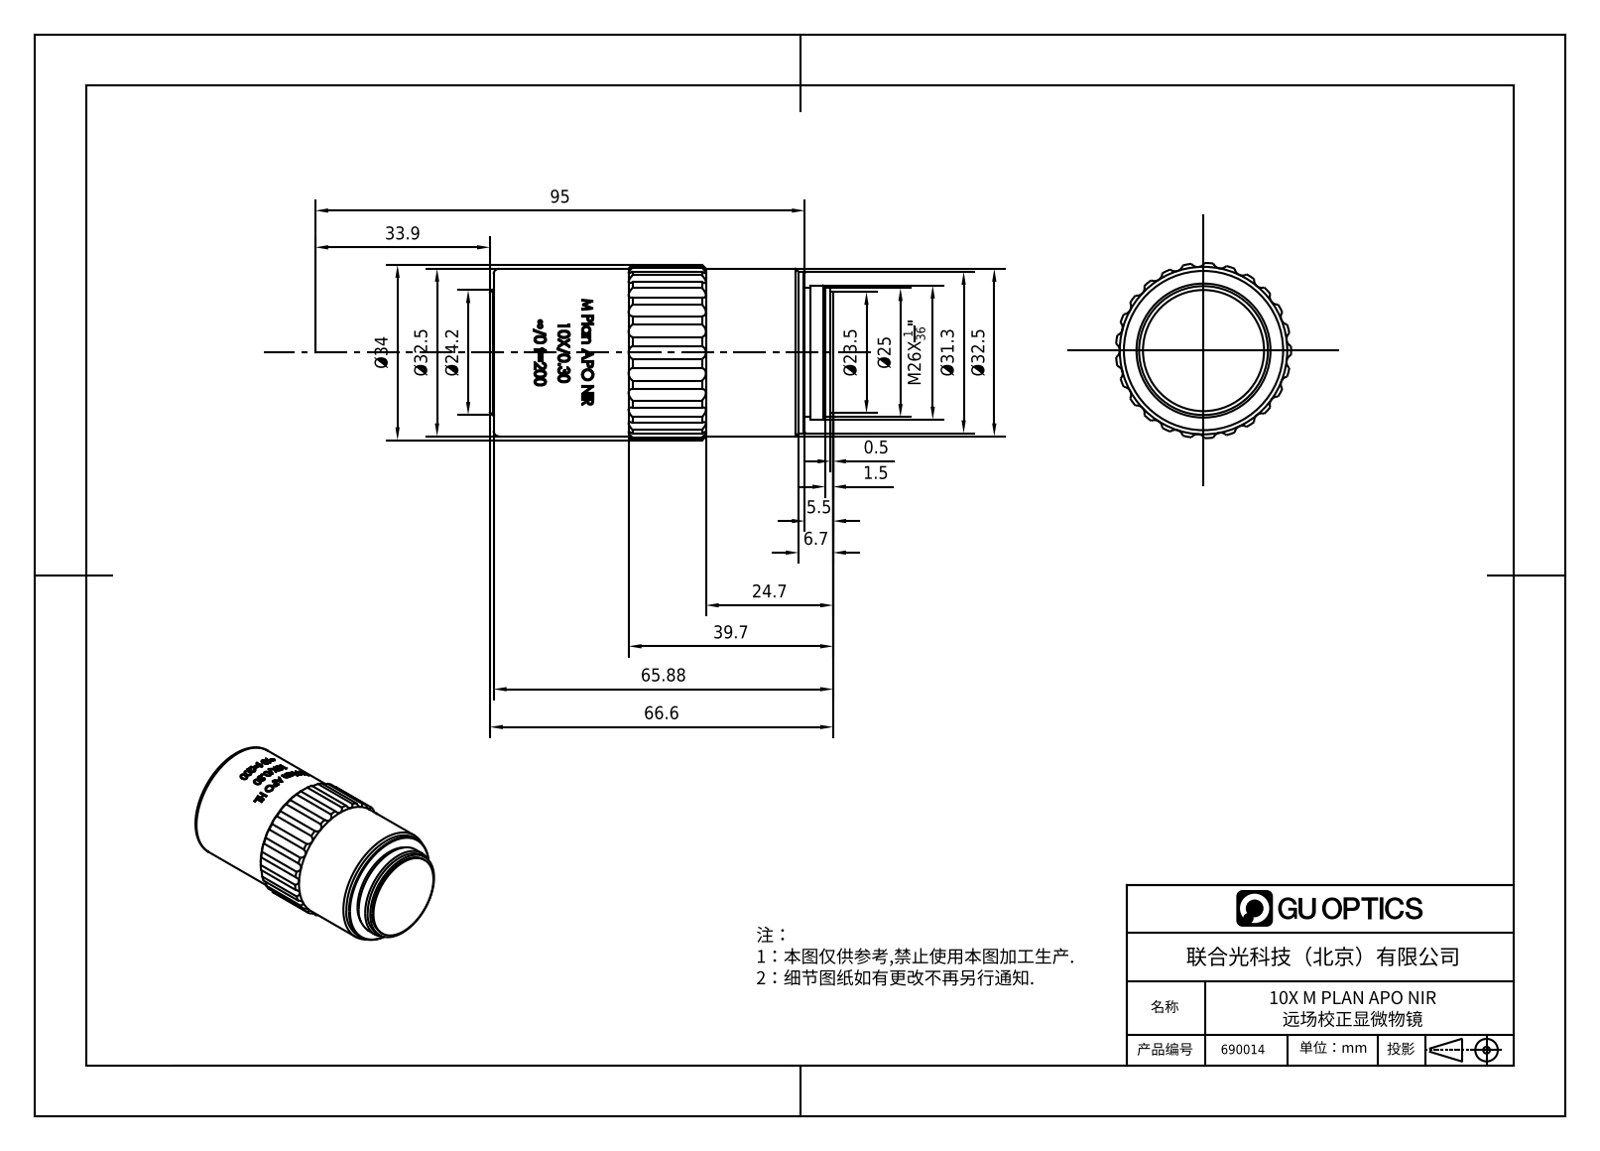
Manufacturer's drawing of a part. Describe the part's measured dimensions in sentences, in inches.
The part is named "690014". Its 3-D file was written by "SolidWorks 2020 (CONFIG_CONTROL_DESIGN)". It is 1 solid with 462 faces: 107 planar, 118 cylindrical and 237 other. Overall it measures 2.622 by 1.339 by 1.337 inches. Its volume is 3.257 cubic inches and its surface area 13.33 square inches. Round holes: 1 of diameter 0.841. Round bosses or shafts: 1 of diameter 1.28, 1 of diameter 1.232, 1 of diameter 1.024, 1 of diameter 0.984, 1 of diameter 0.953, 1 of diameter 0.925. Partial cylindrical surfaces (rounded edges, fillets, slot ends): 25 of radius 0.059, 1 of radius 0.64, 1 of radius 0.669. The main face-to-face distances are 2.583, 2.594, 0.217, 2.377, 2.366, 0.039, 2.406, 0.028, 2.622, 2.602.
